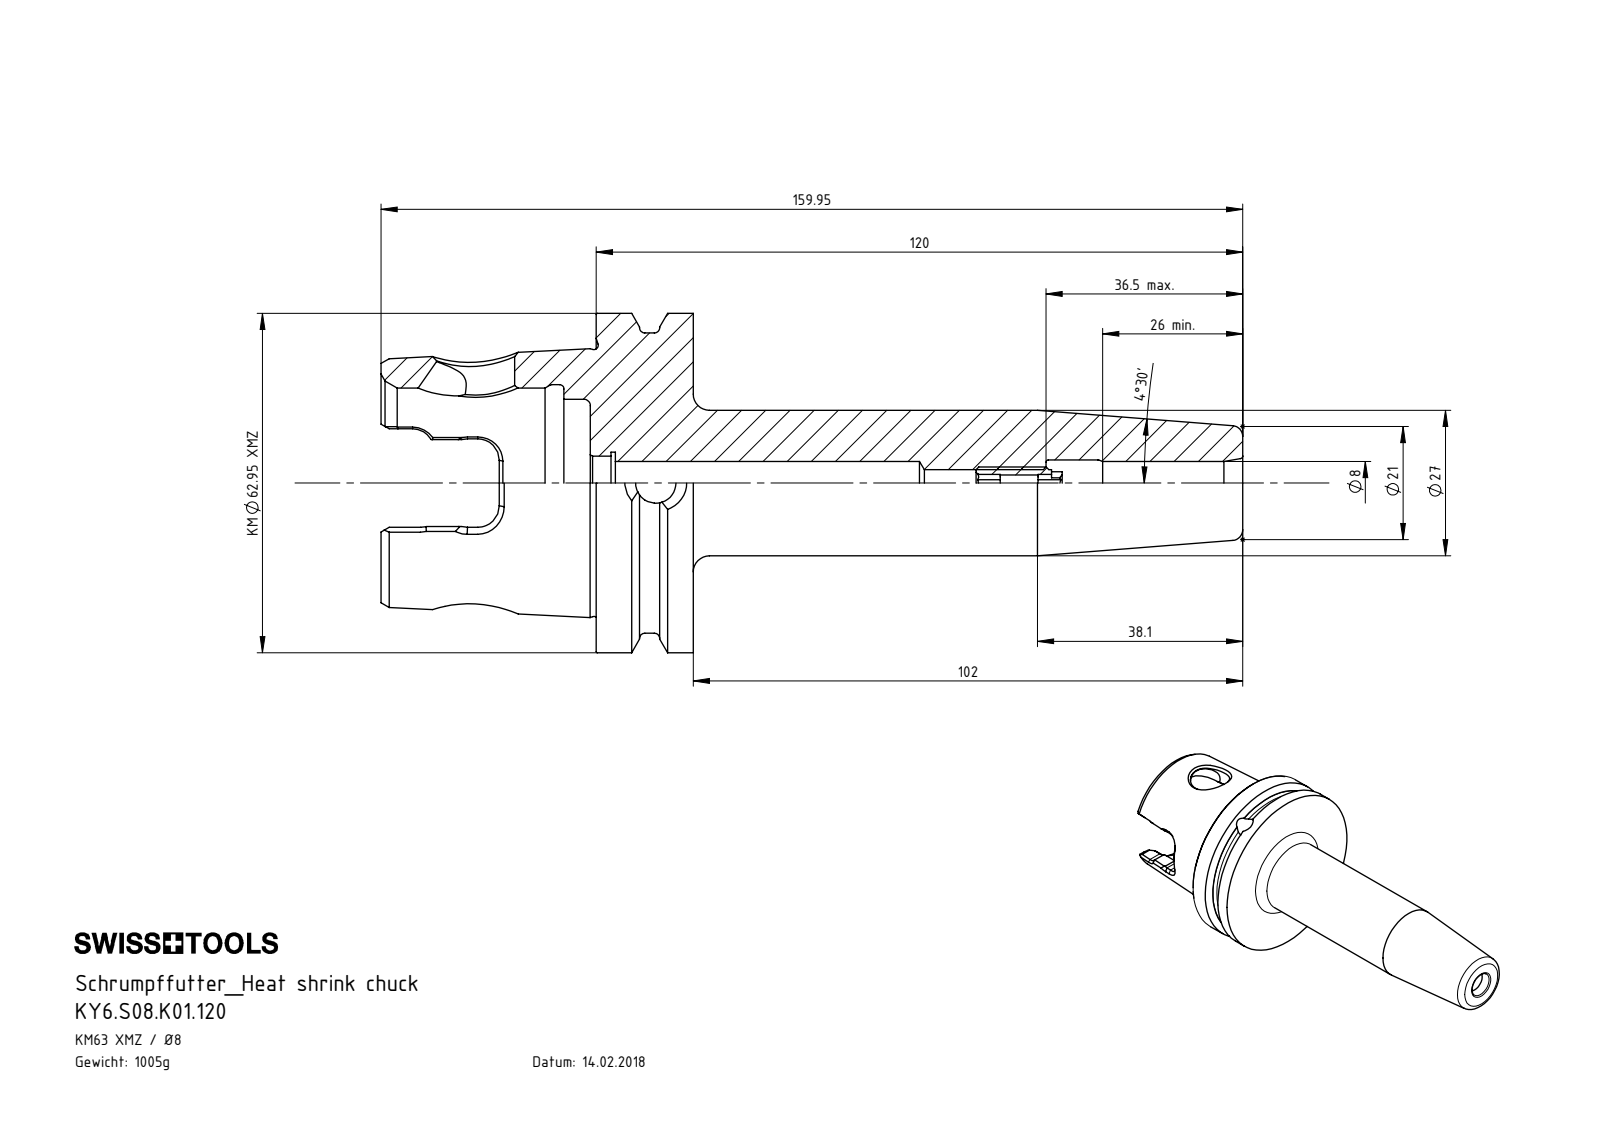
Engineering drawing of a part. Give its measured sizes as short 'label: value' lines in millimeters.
name: ERU-AN2.K01.016_A; KY6-S08.K01.120_A; KY6.S08.K01.120
written by: SolidWorks 2017 (CONFIG_CONTROL_DESIGN)
unit: mm
bodies: 2 solids, 277 faces (79 planar, 60 cylindrical, 138 other)
size: 159.95 × 62.95 × 62.95
volume: 127 993 mm³; area: 30 952 mm²
holes: 2× ⌀7.47, 1× ⌀3, 1× ⌀5, 1× ⌀8, 1× ⌀8.48, 1× ⌀8.6, 1× ⌀10, 1× ⌀11.5, 1× ⌀14.5, 1× ⌀31.1, 1× ⌀35.27, 1× ⌀36.5
bosses: 1× ⌀62.95, 1× ⌀55.7, 1× ⌀27, 1× ⌀6
rounds: 6× R4, 2× R7.04
face distances: 18, 1.1, 19.1, 4.9, 6, 24, 33.95, 38.85, 39.95, 57.95
